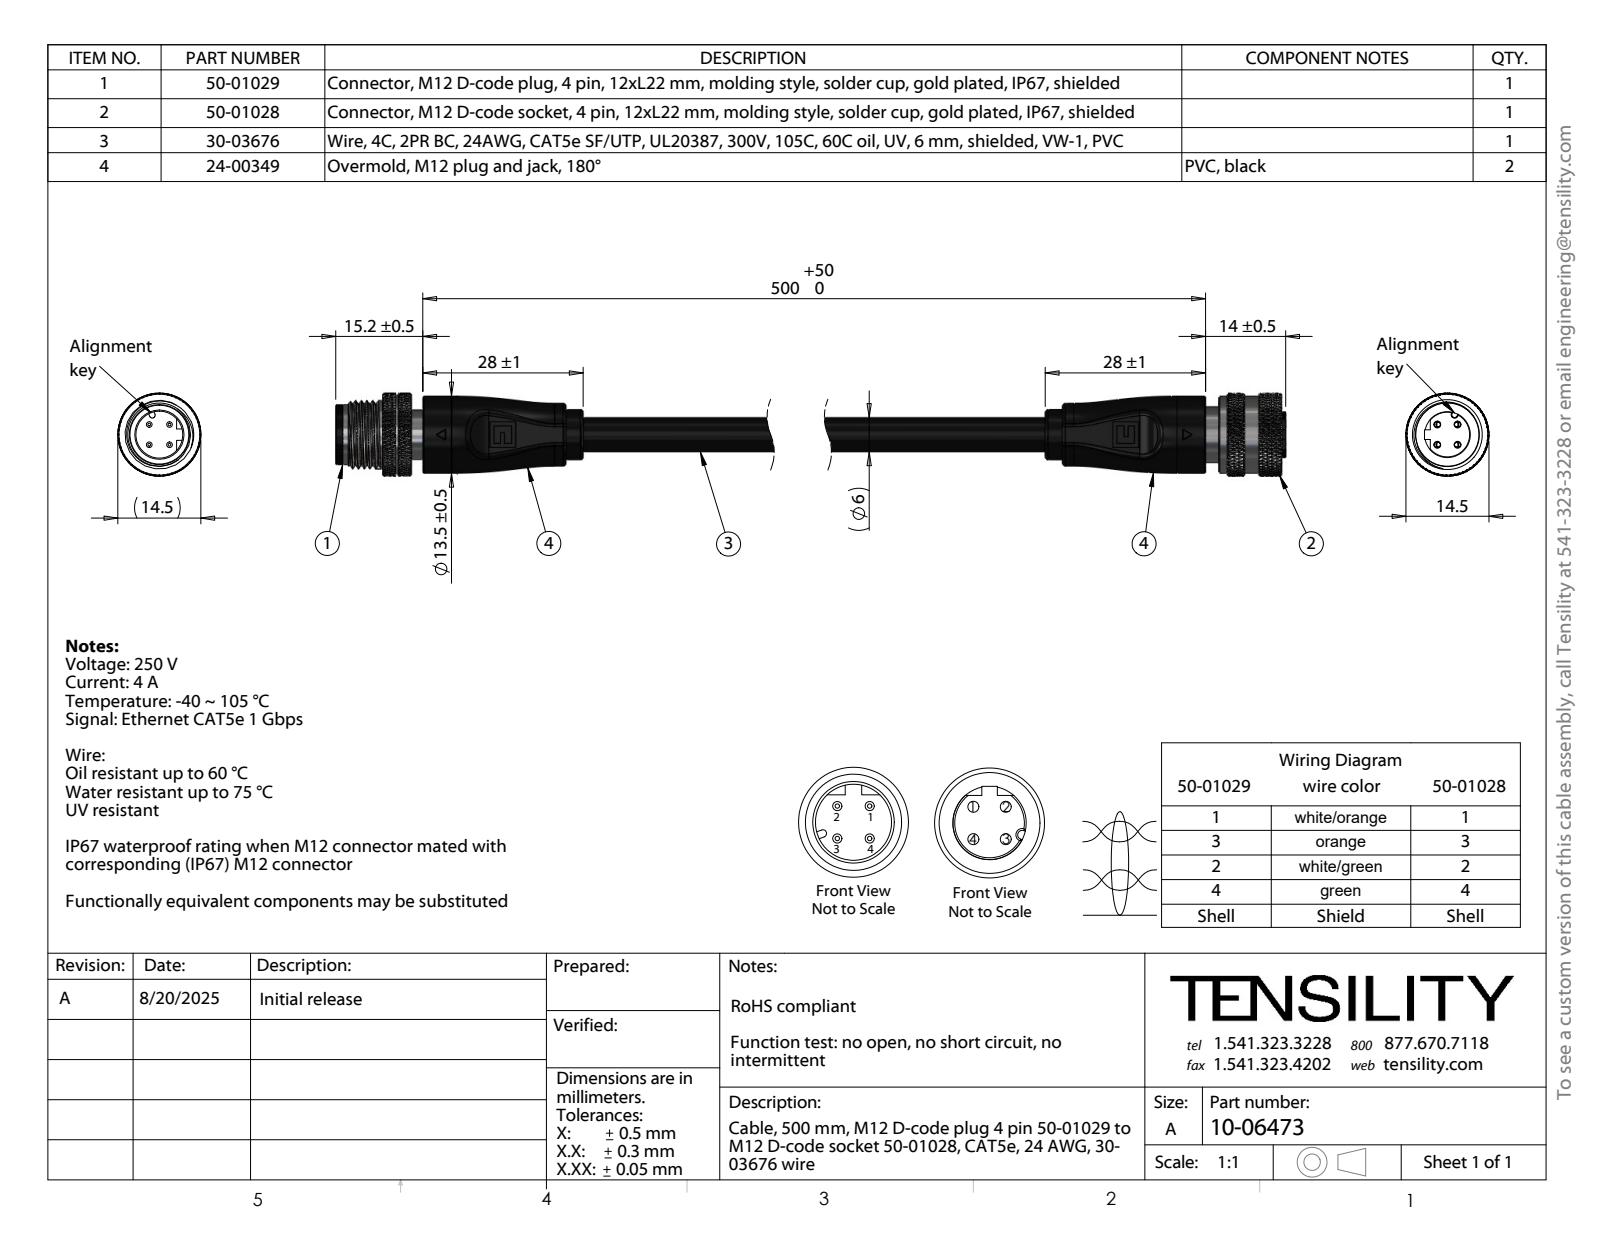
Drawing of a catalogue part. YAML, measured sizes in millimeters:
part_name: "50-01029-04_默认; 50-01028-05_默认; 50-01028-03_默认; 50-01029-03_默认 (+8 more)"
step_written_by: "SolidWorks 2025 (CONFIG_CONTROL_DESIGN)"
units: millimeters
bodies: {solids: 53, faces: 5792, planar: 362, cylindrical: 1477, other: 3953}
overall_size: [235.2, 14.5, 14.5]
volume: 13734
surface_area: 30639
round_holes:
  - {diameter: 0.2, count: 28}
  - {diameter: 1, count: 4}
  - {diameter: 1.05, count: 4}
  - {diameter: 1.1, count: 4}
  - {diameter: 1.2, count: 4}
  - {diameter: 3.16, count: 1}
  - {diameter: 3.21, count: 1}
  - {diameter: 3.56, count: 1}
  - {diameter: 8.2, count: 1}
  - {diameter: 9.5, count: 1}
  - {diameter: 10, count: 1}
  - {diameter: 11.2, count: 1}
round_bosses_or_shafts:
  - {diameter: 1.6, count: 4}
  - {diameter: 1.5, count: 4}
  - {diameter: 1.4, count: 4}
  - {diameter: 14.5, count: 1}
  - {diameter: 13.9, count: 1}
  - {diameter: 13.5, count: 1}
  - {diameter: 12, count: 1}
  - {diameter: 11, count: 1}
partial_cylinders:
  - {radius: 0.1, count: 10}
  - {radius: 0.4, count: 6}
  - {radius: 0.5, count: 4}
  - {radius: 1.5, count: 2}
  - {radius: 1.96, count: 2}
  - {radius: 5, count: 2}
  - {radius: 5.58, count: 1}
  - {radius: 6.75, count: 1}
face_to_face_distances: [206, 7, 28, 178, 2, 208, 3.8, 211.8, 208.3, 5.8]
hole_center_spacings: [1.91, 0.36, 2.09, 1.06, 0.89, 1.08, 1.24, 1.8]
